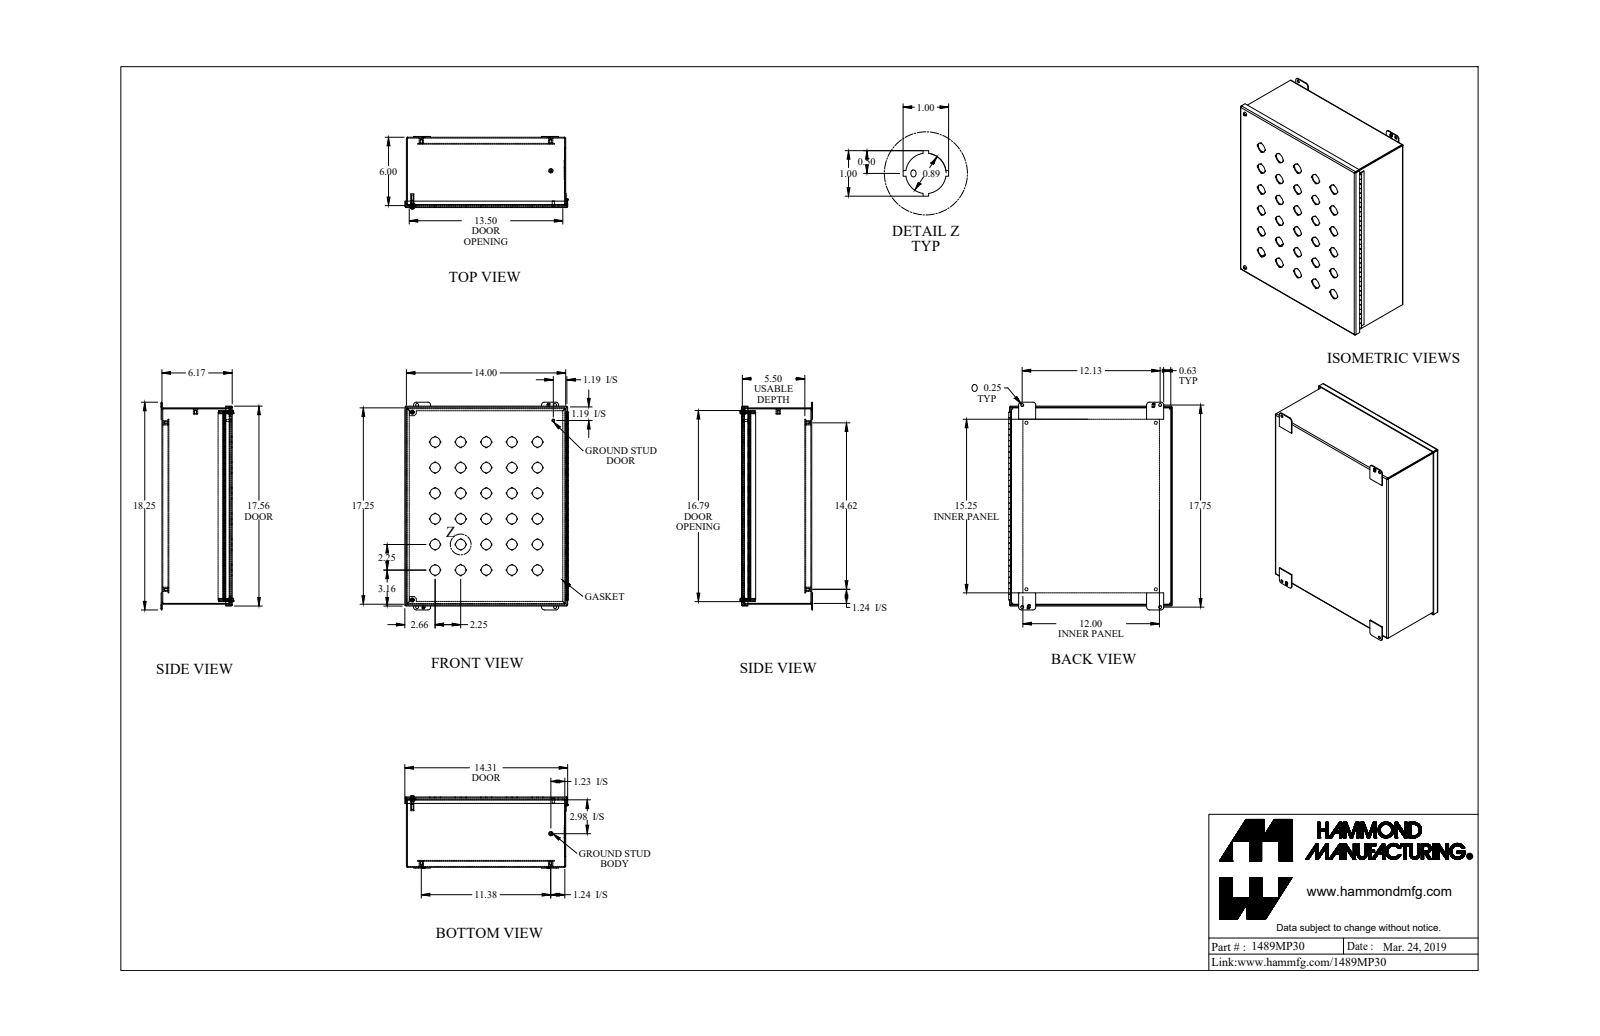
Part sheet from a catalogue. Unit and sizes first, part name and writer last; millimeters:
Units: millimetres
Overall size (bounding box): 463.6 × 365.1 × 161.8
Round holes (diameter × count): ⌀22.5 ×30, ⌀6.4 ×6, ⌀4 ×5, ⌀6.7 ×4, ⌀4 ×2, ⌀10.3 ×2
Round bosses / shafts (diameter × count): ⌀9.5 ×5, ⌀9.9 ×2, ⌀7 ×2, ⌀4.8 ×2, ⌀3.8 ×2, ⌀6.4 ×1, ⌀4.8 ×1, ⌀4.4 ×1
Partial cylindrical surfaces — rounded edges, fillets, slot ends (radius × count): R0.9 ×12, R2.7 ×12, R6.4 ×8, R4.1 ×2, R4.3 ×2
Main face-to-face distances: 1.8, 154.9, 141.4, 13.5, 153.1, 156.8, 353.8, 15.3, 143.3, 11.7
Hole centre spacings: 127.8, 57.2, 80.8, 180.7, 114.3, 206.1, 171.5, 161.6
Volume: 1 421 000 mm³ · Surface area: 1 506 000 mm²
Bodies: 21 solids, 1277 faces (894 planar, 325 cylindrical, 58 other)
Part name (STEP PRODUCT): 1489MP30_Default
STEP written by: SolidWorks 2019 (CONFIG_CONTROL_DESIGN)
